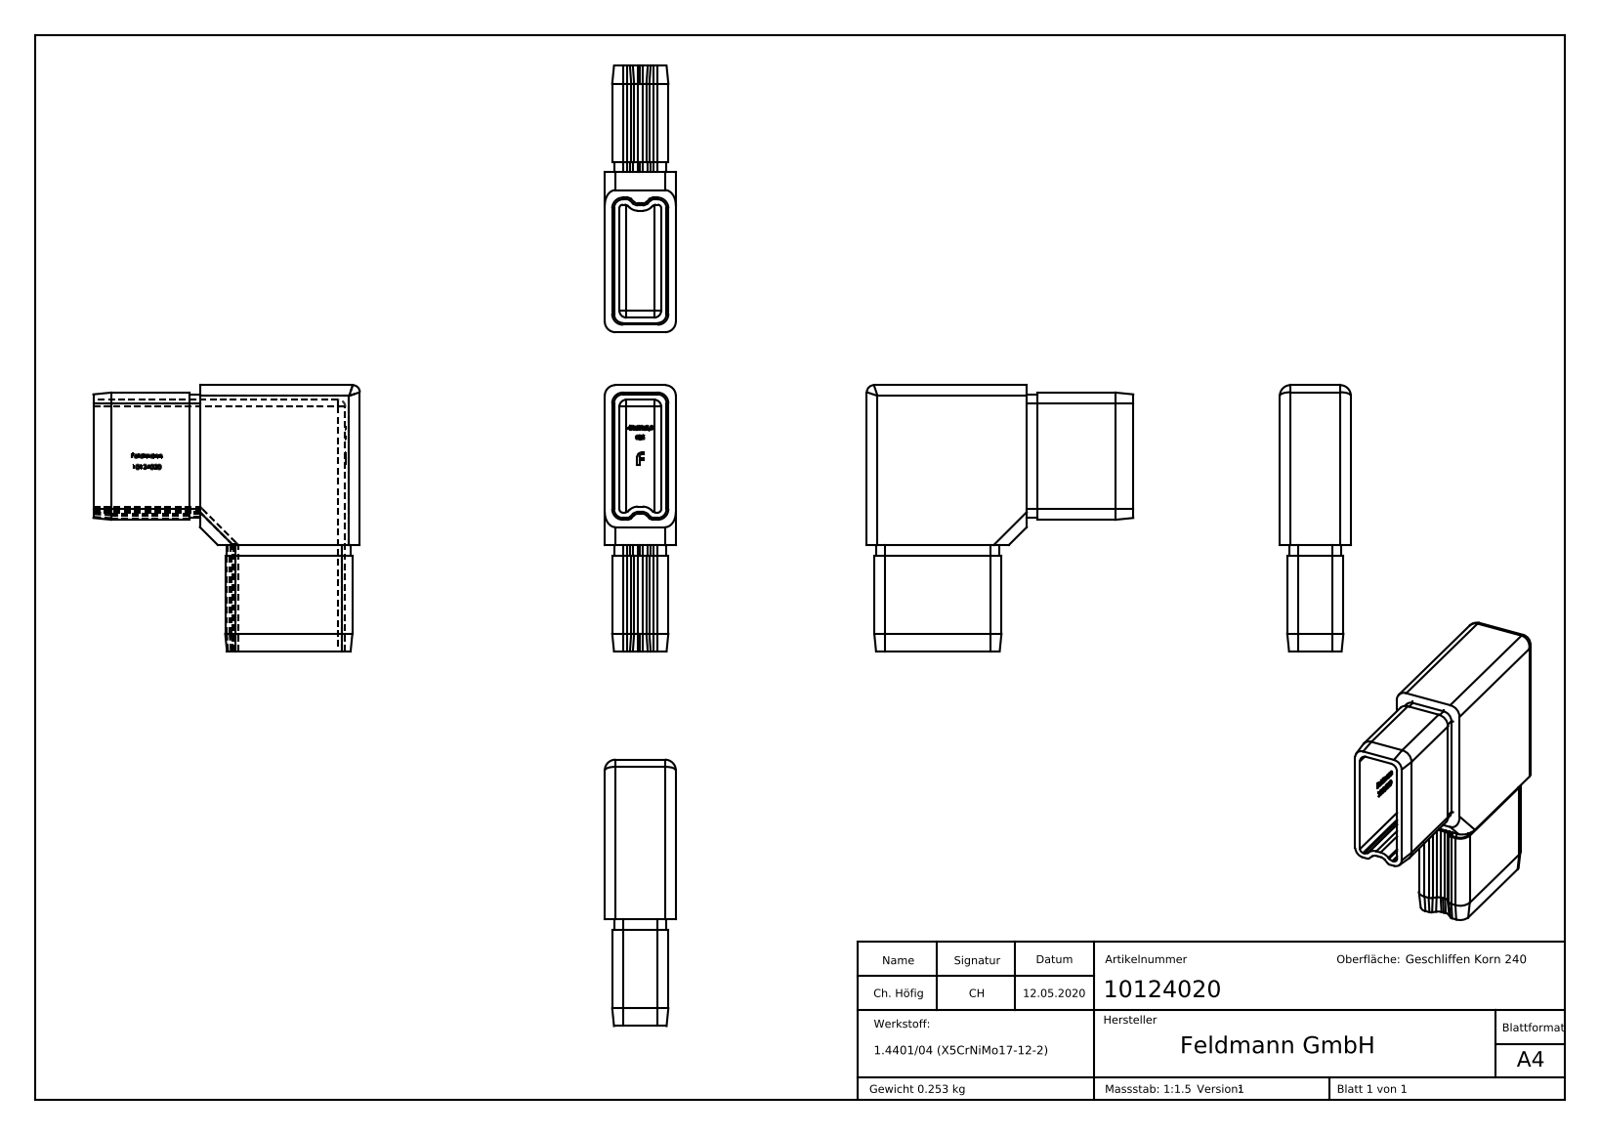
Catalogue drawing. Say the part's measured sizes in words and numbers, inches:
The part is named "10124020". Its 3-D file was written by "SolidWorks 2015 (CONFIG_CONTROL_DESIGN)". It is 1 solid with 548 faces: 320 planar, 56 cylindrical and 172 other. Overall it measures 2.953 by 2.953 by 0.787 inches. Its volume is 1.93 cubic inches and its surface area 34.01 square inches. Partial cylindrical surfaces (rounded edges, fillets, slot ends): 14 of radius 0.118, 12 of radius 0.059, 10 of radius 0.079, 8 of radius 0.039, 8 of radius 0.098, 4 of radius 0.138. The main face-to-face distances are 0.161, 0.626, 0.465, 0.079, 0.083, 0.543, 0.705, 0.787, 0.622, 1.772.
